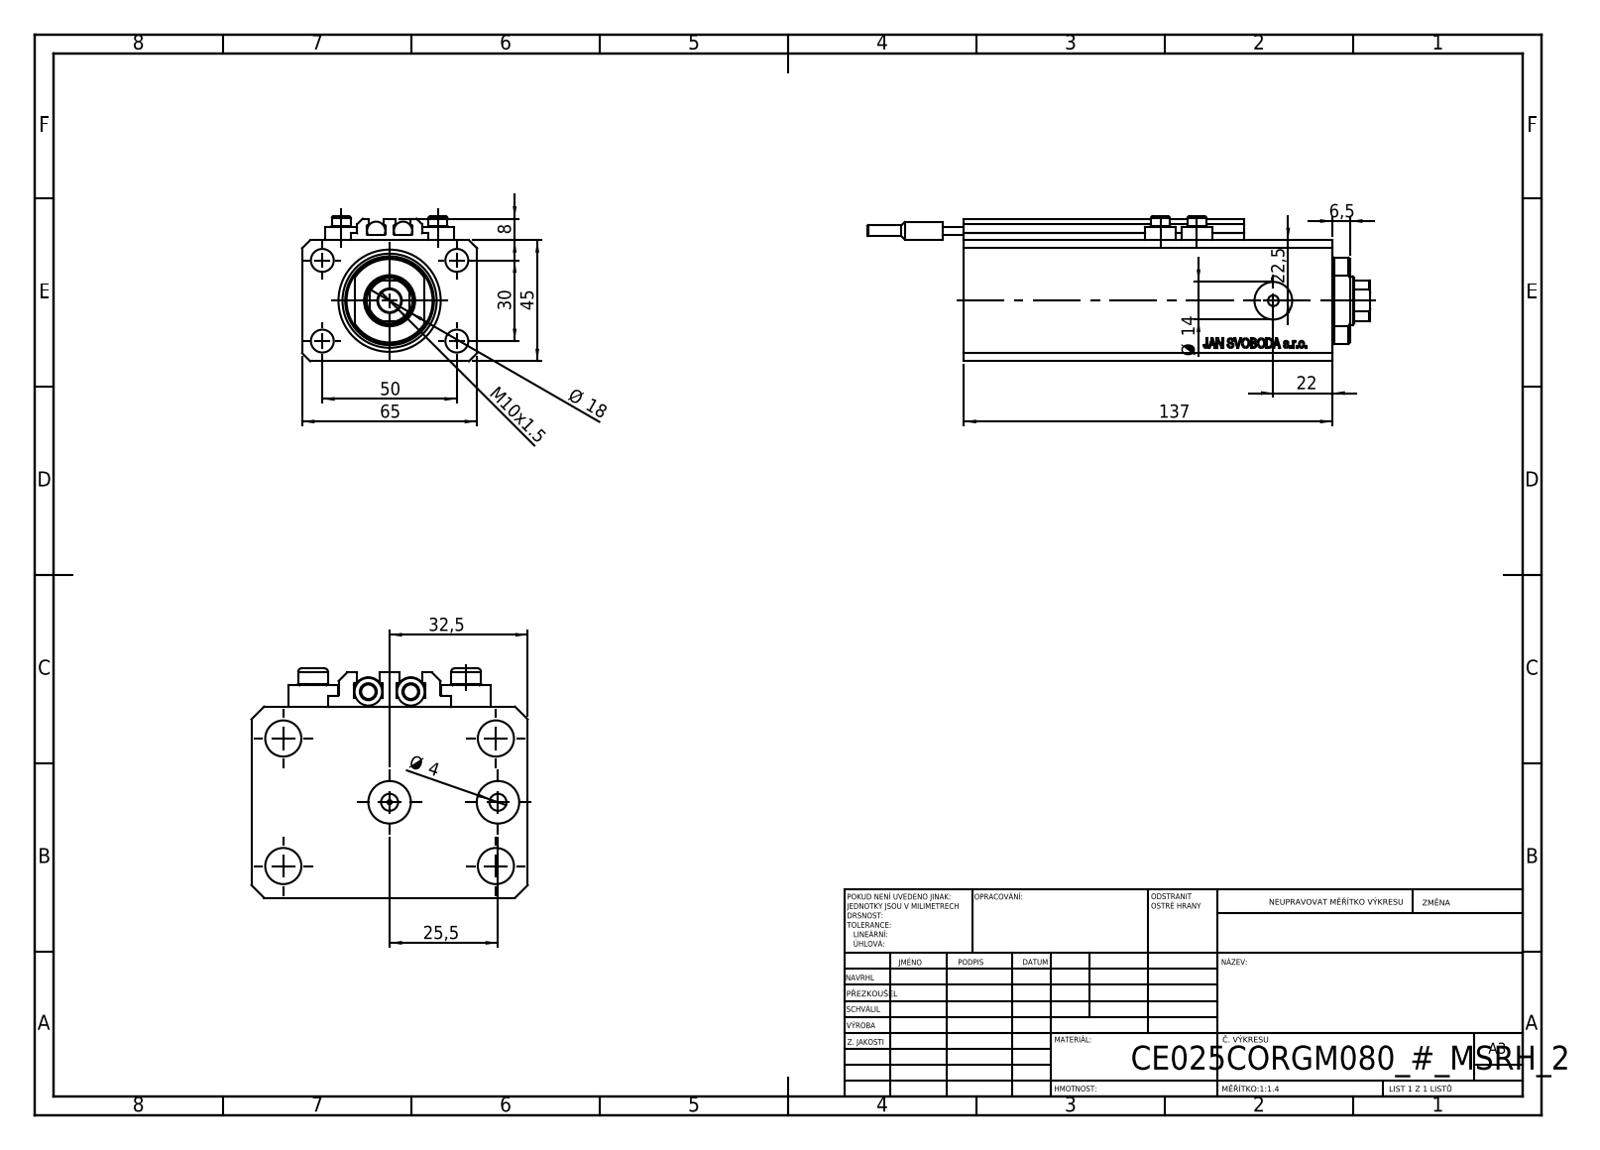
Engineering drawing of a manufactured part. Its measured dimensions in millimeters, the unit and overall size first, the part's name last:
Units: millimetres
Overall size (bounding box): 187 × 65 × 54
Round holes (diameter × count): ⌀4 ×8, ⌀8.5 ×5, ⌀10 ×2, ⌀14 ×2, ⌀1.25 ×1, ⌀18 ×1, ⌀25 ×1, ⌀38 ×1
Round bosses / shafts (diameter × count): ⌀11.6 ×4, ⌀7 ×4, ⌀6.8 ×2, ⌀6.5 ×2, ⌀4 ×2
Partial cylindrical surfaces — rounded edges, fillets, slot ends (radius × count): R0.2 ×10, R8.5 ×1, R16 ×1
Main face-to-face distances: 45, 65, 47, 14, 137, 2, 123, 2.5, 3, 10
Hole centre spacings: 29.15, 13.6, 15.01, 30, 36, 38.48, 50, 52.68
Volume: 369 219 mm³ · Surface area: 93 835 mm²
Bodies: 10 solids, 1090 faces (536 planar, 100 cylindrical, 454 other)
Part name (STEP PRODUCT): SWITCH_V250CE; V250CE_C_Body; ALLEN BOLT V250CE; V250CE_C_VCP (+1 more)
STEP written by: SolidWorks 2019 (CONFIG_CONTROL_DESIGN)
